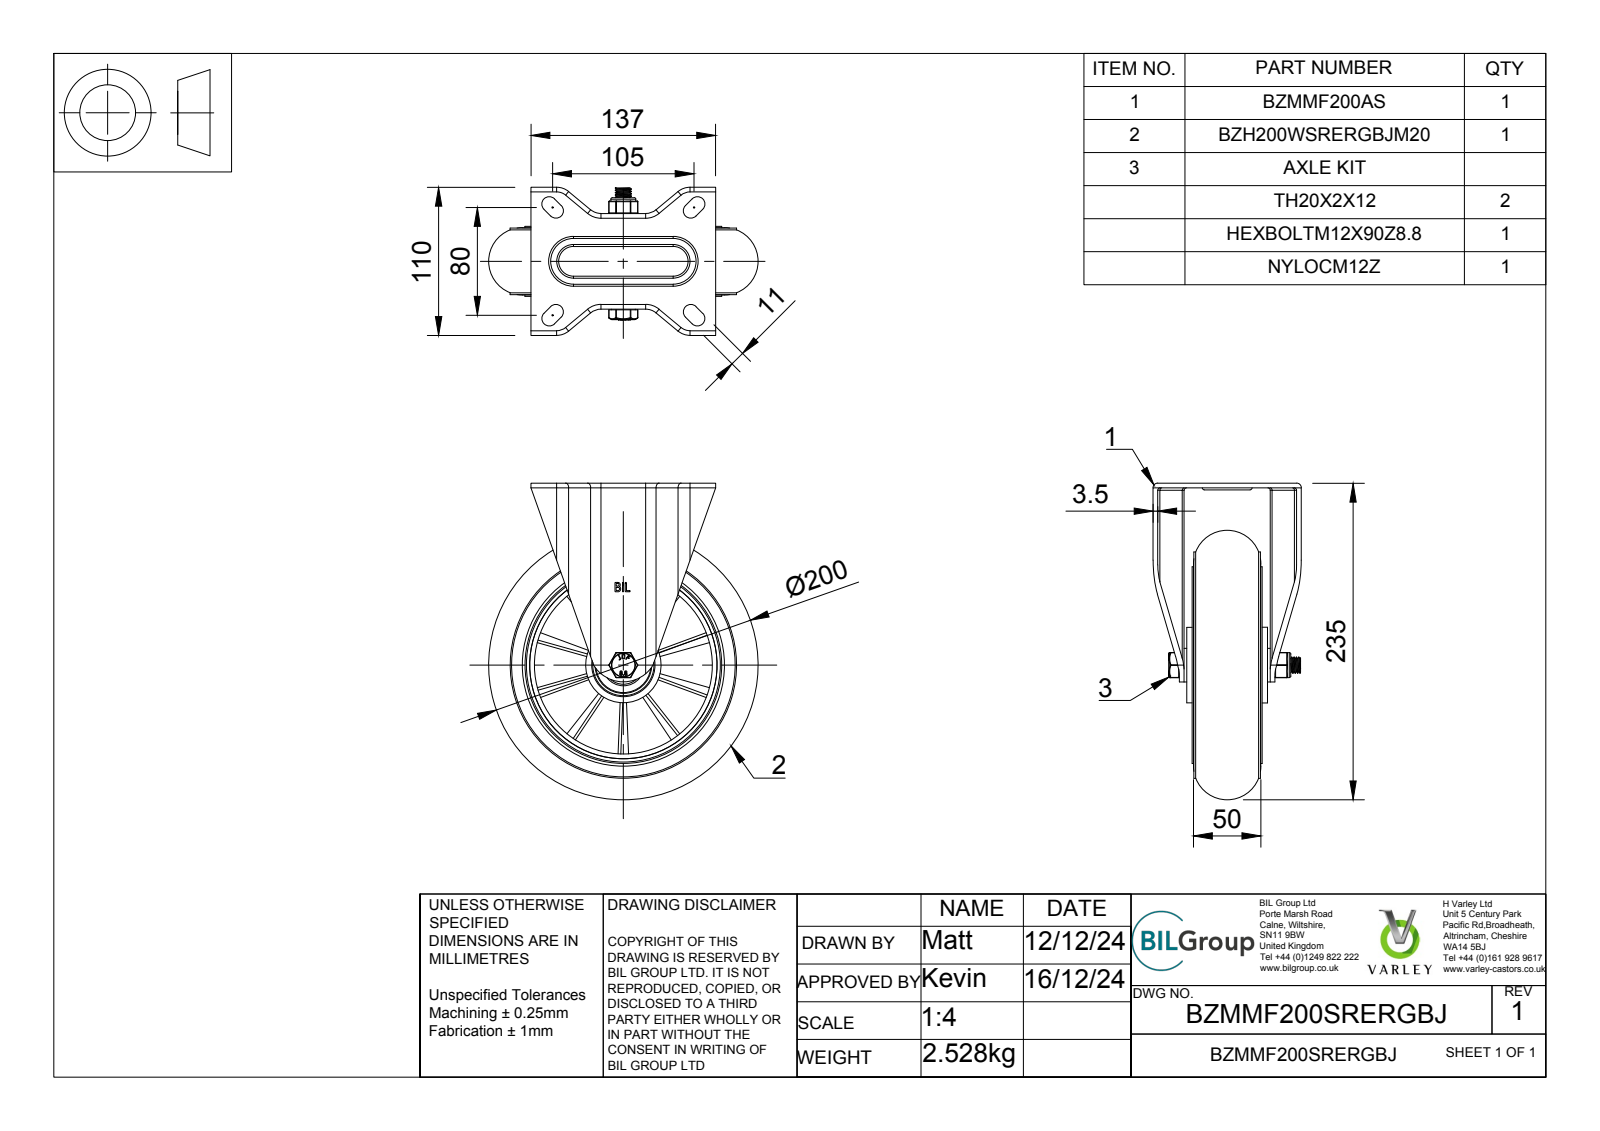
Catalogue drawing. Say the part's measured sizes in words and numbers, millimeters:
The part is named "BZMMF200SRERGBJ v4; BZMMF200AS - 64 v1; ZINC PLATED, PRESSED STEEL BRACKET; BZH200WSRERGBJM20 v1 (+8 more)". Its 3-D file was written by "Autodesk Translation Framework v13.20.0.188 (AP242_MANAGED_MODEL_BASED_3D_ENGINEERING_MIM_LF)". It is 35 solids with 1173 faces: 459 planar, 240 cylindrical and 474 other. Overall it measures 235 by 200 by 110 millimeters. Its volume is 1 018 000 cubic millimeters and its surface area 315 992 square millimeters. Round holes: 1 of diameter 12, 1 of diameter 12.2, 1 of diameter 14, 1 of diameter 20, 1 of diameter 28.5, 1 of diameter 30.8, 1 of diameter 40.3, 1 of diameter 40.5, 1 of diameter 42, 1 of diameter 47, 1 of diameter 132, 1 of diameter 139. Round bosses or shafts: 1 of diameter 168, 1 of diameter 146, 1 of diameter 56.2, 1 of diameter 56, 1 of diameter 40.8, 1 of diameter 31.3, 1 of diameter 27, 1 of diameter 25. Partial cylindrical surfaces (rounded edges, fillets, slot ends): 19 of radius 0.5, 8 of radius 1.5, 8 of radius 1.75, 8 of radius 3.5, 8 of radius 5.5, 4 of radius 0.47, 4 of radius 0.9, 4 of radius 6. The main face-to-face distances are 3.5, 14.25, 2, 47.75, 67.5, 17.75, 53.25, 49.75, 19.75, 51.25.
